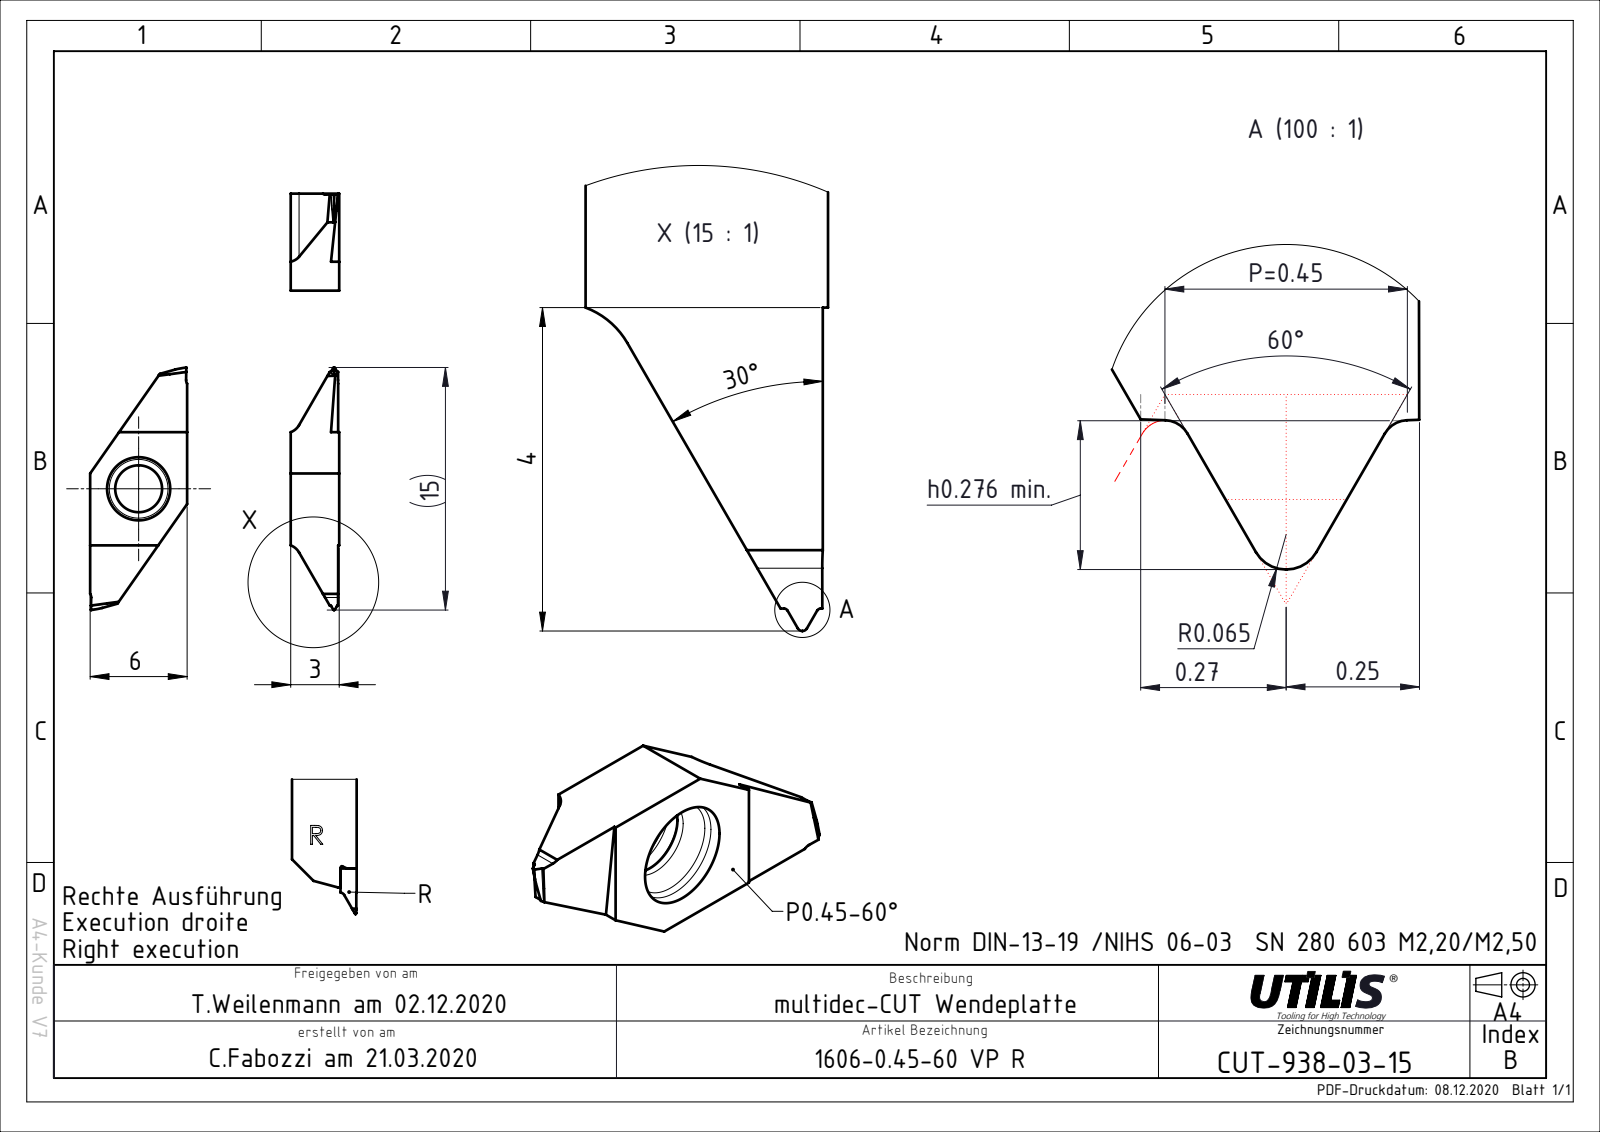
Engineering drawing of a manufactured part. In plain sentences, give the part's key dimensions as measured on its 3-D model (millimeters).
The part is named "CUT-938-03; ASME Y14.5". Its 3-D file was written by "FormatWorks Professional (AP242_MANAGED_MODEL_BASED_3D_ENGINEERING_MIM_LF)". It is 1 solid with 40 faces: 22 planar, 14 cylindrical and 4 other. Overall it measures 15 by 6 by 3 millimeters. Its volume is 130 cubic millimeters and its surface area 212 square millimeters. Round holes: 1 of diameter 2.9. Partial cylindrical surfaces (rounded edges, fillets, slot ends): 2 of radius 1. The main face-to-face distances are 6, 3, 9, 12, 7, 11.18, 11.17, 12.97.
